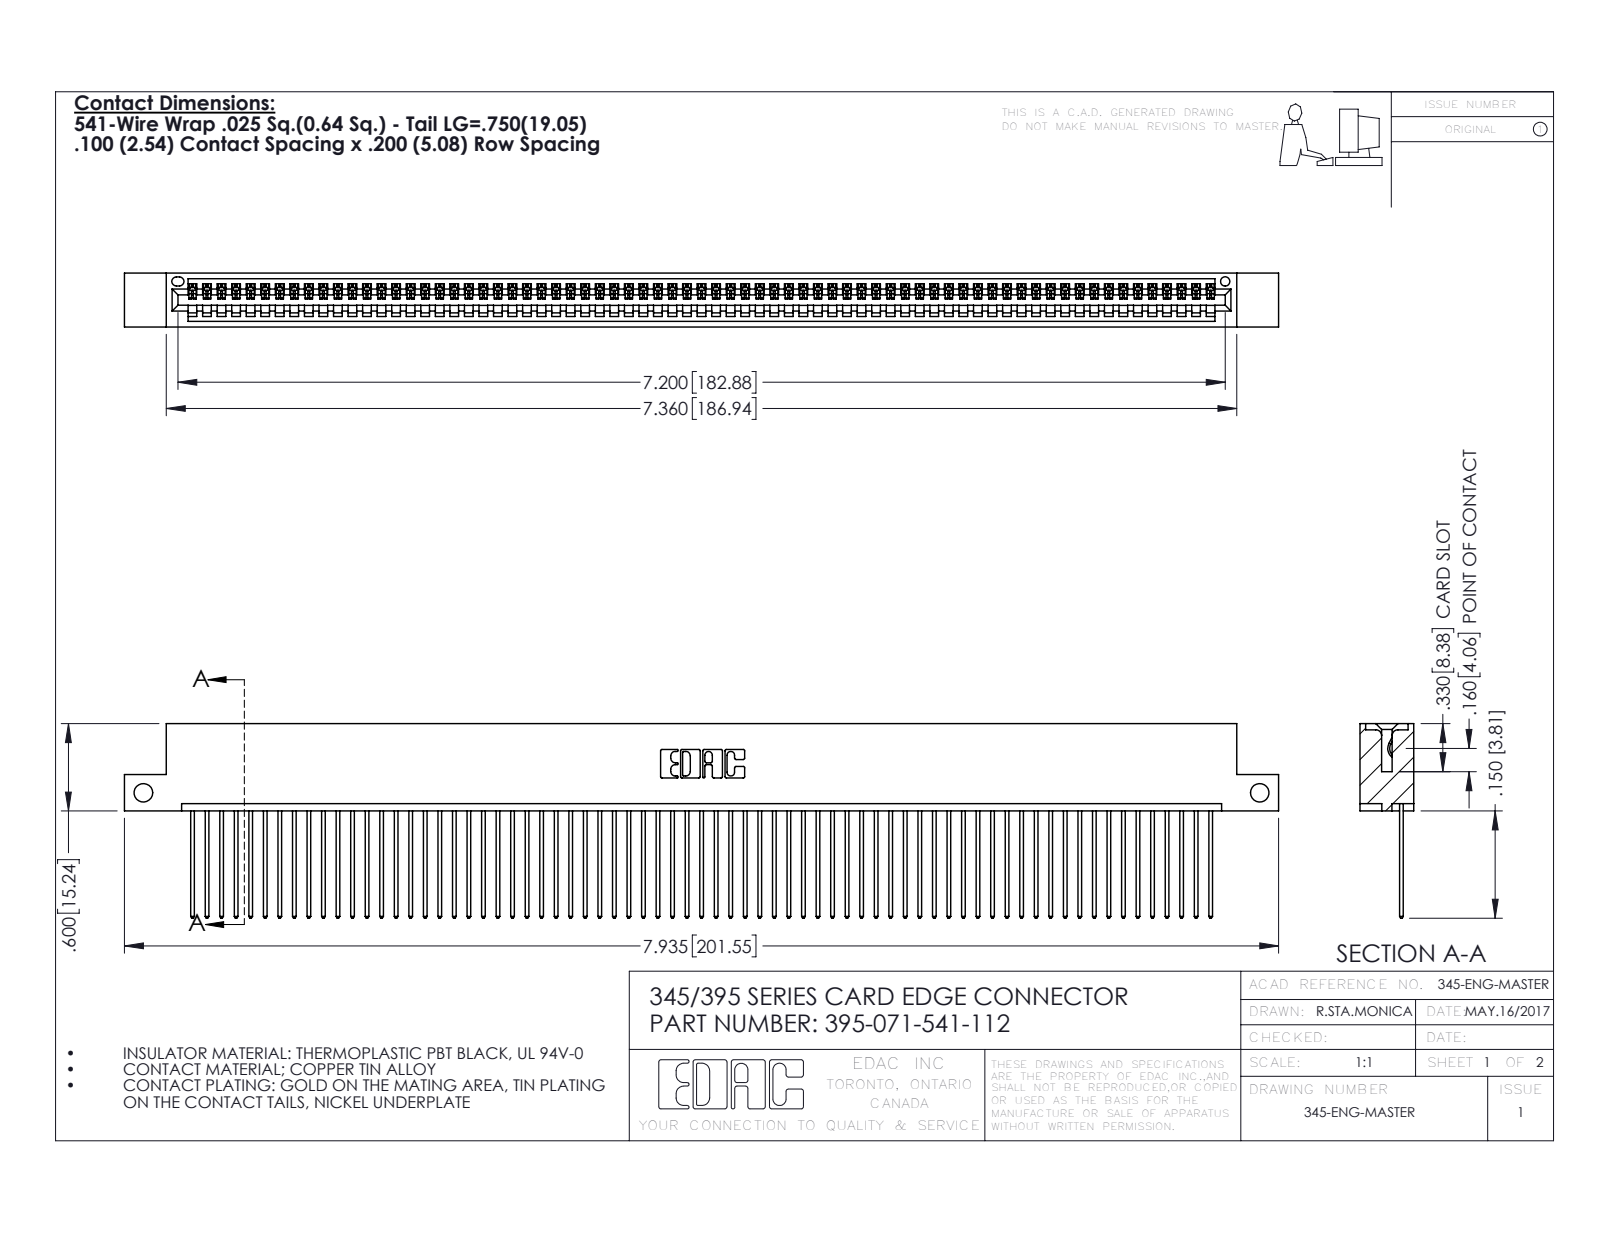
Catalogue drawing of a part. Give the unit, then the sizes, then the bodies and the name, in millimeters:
Units: millimetres
Overall size (bounding box): 201.5 × 34 × 9.4
Round holes (diameter × count): ⌀3.3 ×2, ⌀1.6 ×1
Partial cylindrical surfaces — rounded edges, fillets, slot ends (radius × count): R0.2 ×142, R0.3 ×142, R0.3 ×22, R0.2 ×6, R0.8 ×6, R0.7 ×3, R0.8 ×2, R1 ×2
Main face-to-face distances: 1.8, 7.6, 2.5, 6.9, 0.6, 9.4, 5.1, 5.7, 3.8, 1.8
Hole centre spacings: 194.9
Volume: 19 530 mm³ · Surface area: 27 580 mm²
Bodies: 72 solids, 4244 faces (2920 planar, 1324 cylindrical, 0 other)
Part name (STEP PRODUCT): 345-292-001_345-293-141; 395-071-541-112; 345 Part_Flush Mounting Lugs - Side Mount
STEP written by: SolidWorks 2016 (CONFIG_CONTROL_DESIGN)
